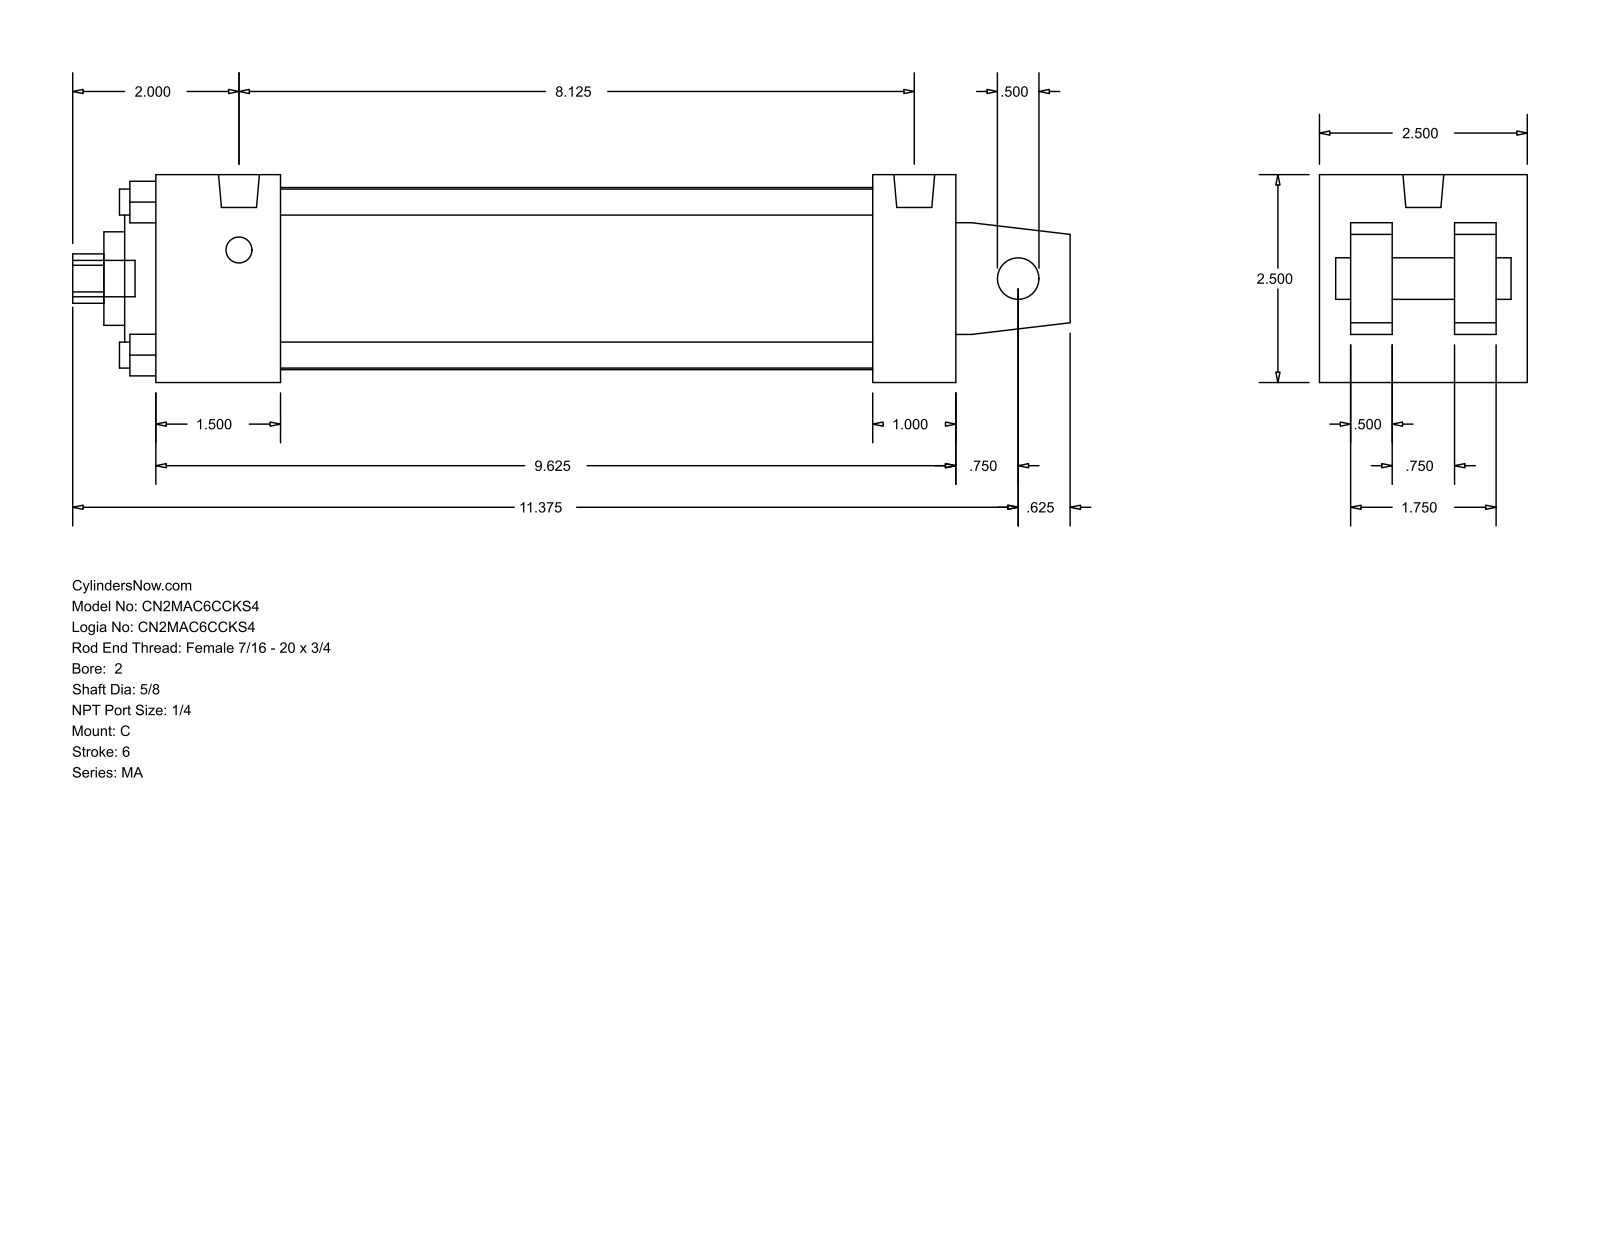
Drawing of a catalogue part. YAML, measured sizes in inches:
part_name: "MA_C__0200_0.625"
step_written_by: "GSSL Pune (CONFIG_CONTROL_DESIGN)"
units: inches
bodies: {solids: 0, faces: 105, planar: 77, cylindrical: 28, other: 0}
overall_size: [12, 2.5, 2.5]
round_holes:
  - {diameter: 0.313, count: 4}
  - {diameter: 0.5, count: 1}
  - {diameter: 0.625, count: 1}
  - {diameter: 1.125, count: 1}
  - {diameter: 2, count: 1}
  - {diameter: 2.19, count: 1}
round_bosses_or_shafts:
  - {diameter: 0.313, count: 4}
  - {diameter: 0.492, count: 2}
  - {diameter: 0.437, count: 1}
partial_cylinders:
  - {radius: 0.297, count: 1}
face_to_face_distances: [2.5, 0.375, 0.5, 0.875, 1.625, 2.125, 1.25, 1.5, 9.625, 8.125]
hole_center_spacings: [1.301, 1.84, 2.602]
